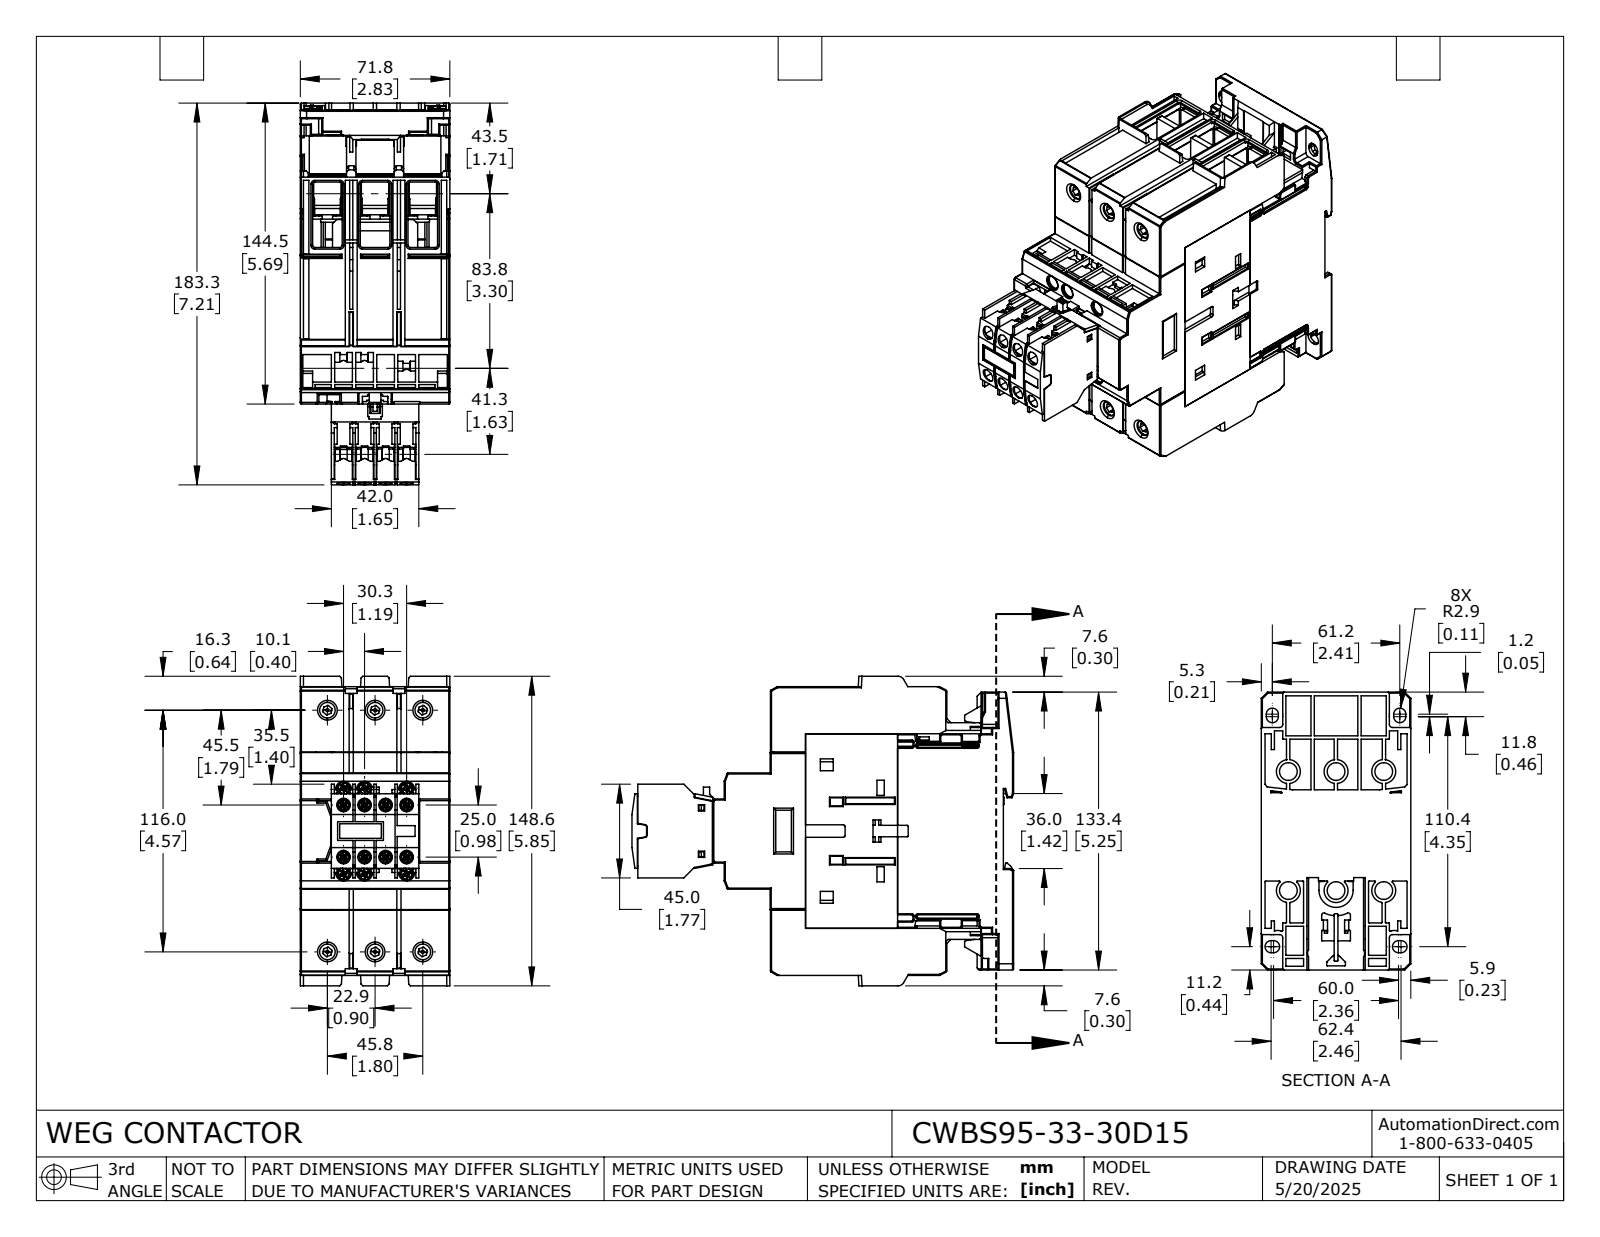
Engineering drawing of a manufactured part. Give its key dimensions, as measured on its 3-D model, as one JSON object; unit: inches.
{"part_name": "CWBS95-33-30D15", "step_written_by": "SolidWorks 2024 (AUTOMOTIVE_DESIGN)", "units": "inches", "bodies": {"solids": 42, "faces": 7161, "planar": 4791, "cylindrical": 1513, "other": 857}, "overall_size": [7.215, 5.85, 2.827], "volume_in3": 54.55, "surface_area_in2": 511.4, "round_holes": [[0.165, 10], [0.13, 8], [0.256, 8], [0.114, 6], [0.264, 6], [0.276, 6], [0.295, 6], [0.335, 6], [0.374, 6], [0.287, 4], [0.124, 1]], "round_bosses_or_shafts": [[0.138, 8], [0.366, 6], [0.313, 6], [0.14, 6], [0.453, 5], [0.107, 5], [0.107, 3], [0.276, 2]], "partial_cylinders_radius": [[0.02, 274], [0.012, 156], [0.016, 113], [0.004, 64], [0.039, 49], [0.024, 36], [0.059, 24], [0.031, 14]], "face_to_face_distances": [0.059, 0.902, 2.827, 1.835, 0.874, 0.992, 0.933, 0.118, 1.776, 1.894], "hole_center_spacings": [0.902, 1.469, 3.525, 1.159, 1.535, 3.408, 0.398, 0.455]}
